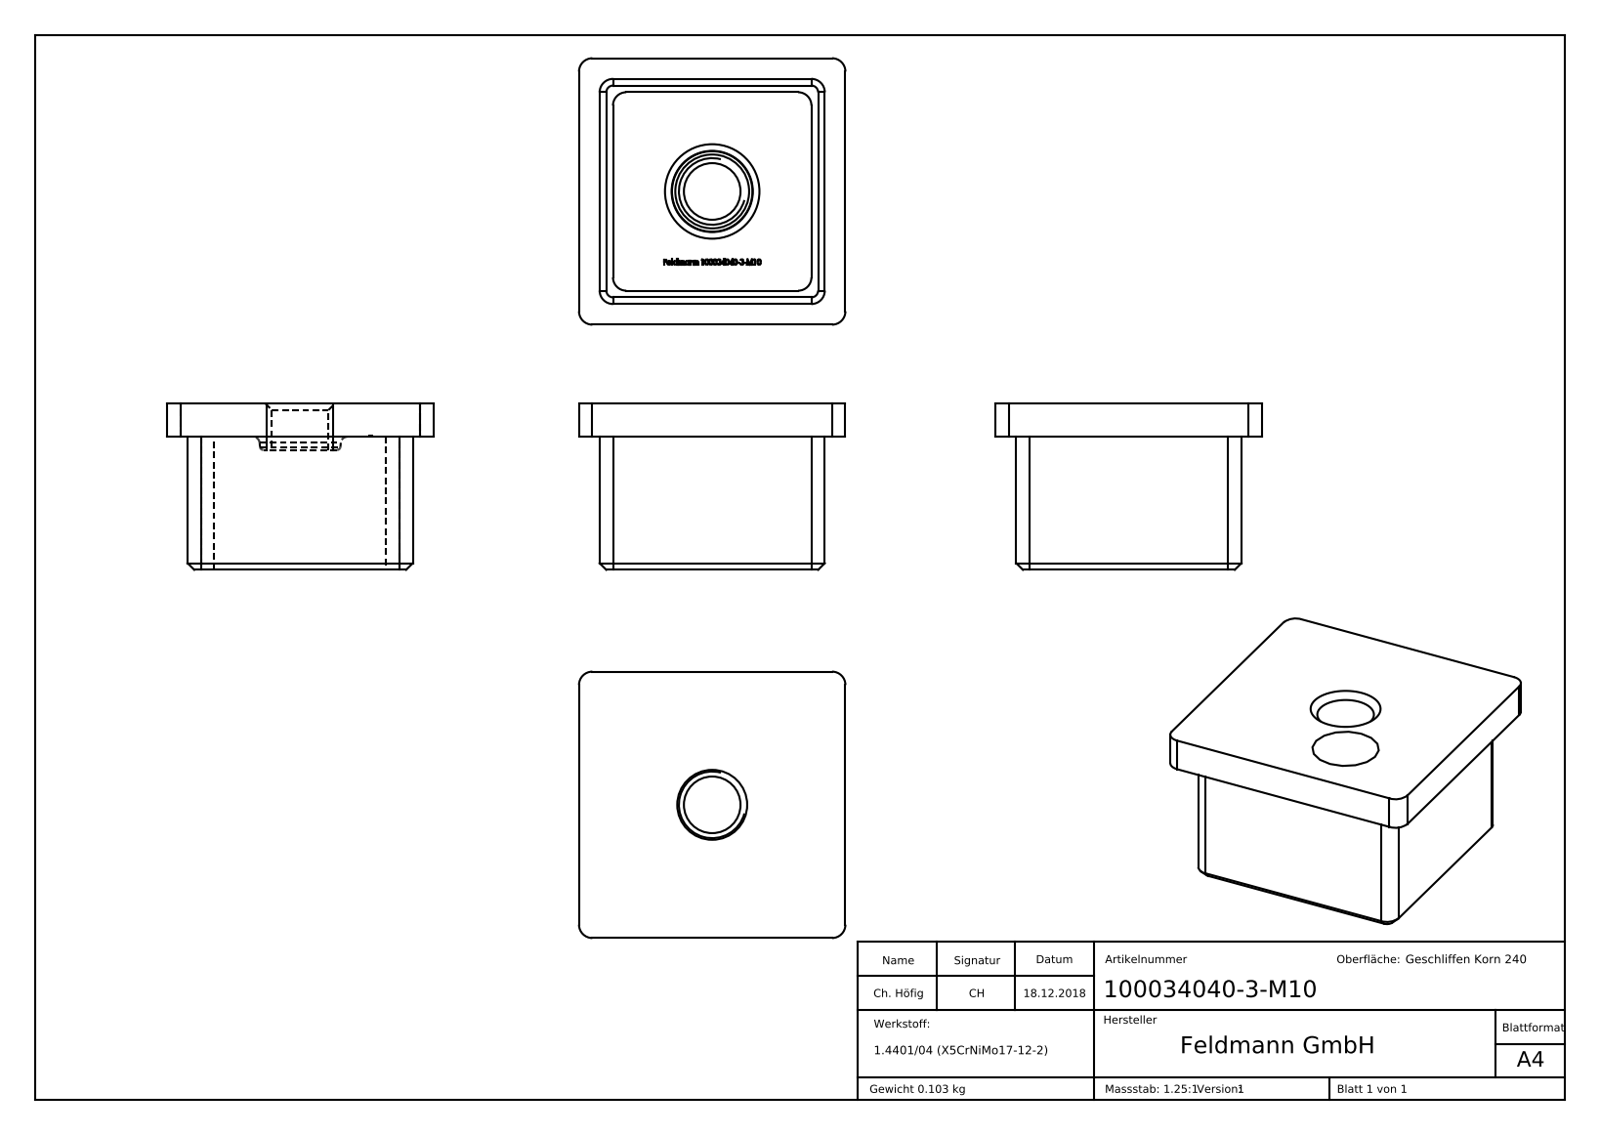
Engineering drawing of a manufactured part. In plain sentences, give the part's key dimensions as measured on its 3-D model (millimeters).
The part is named "100034040-3-M10". Its 3-D file was written by "SolidWorks 2015 (CONFIG_CONTROL_DESIGN)". It is 1 solid with 330 faces: 174 planar, 14 cylindrical and 142 other. Overall it measures 40 by 40 by 25 millimeters. Its volume is 12 832 cubic millimeters and its surface area 8 965 square millimeters. Round holes: 1 of diameter 8.5. Partial cylindrical surfaces (rounded edges, fillets, slot ends): 12 of radius 2. The main face-to-face distances are 2, 31.8, 5, 33.8, 29.8, 5.1, 3.1, 34.9, 36.9, 40.
